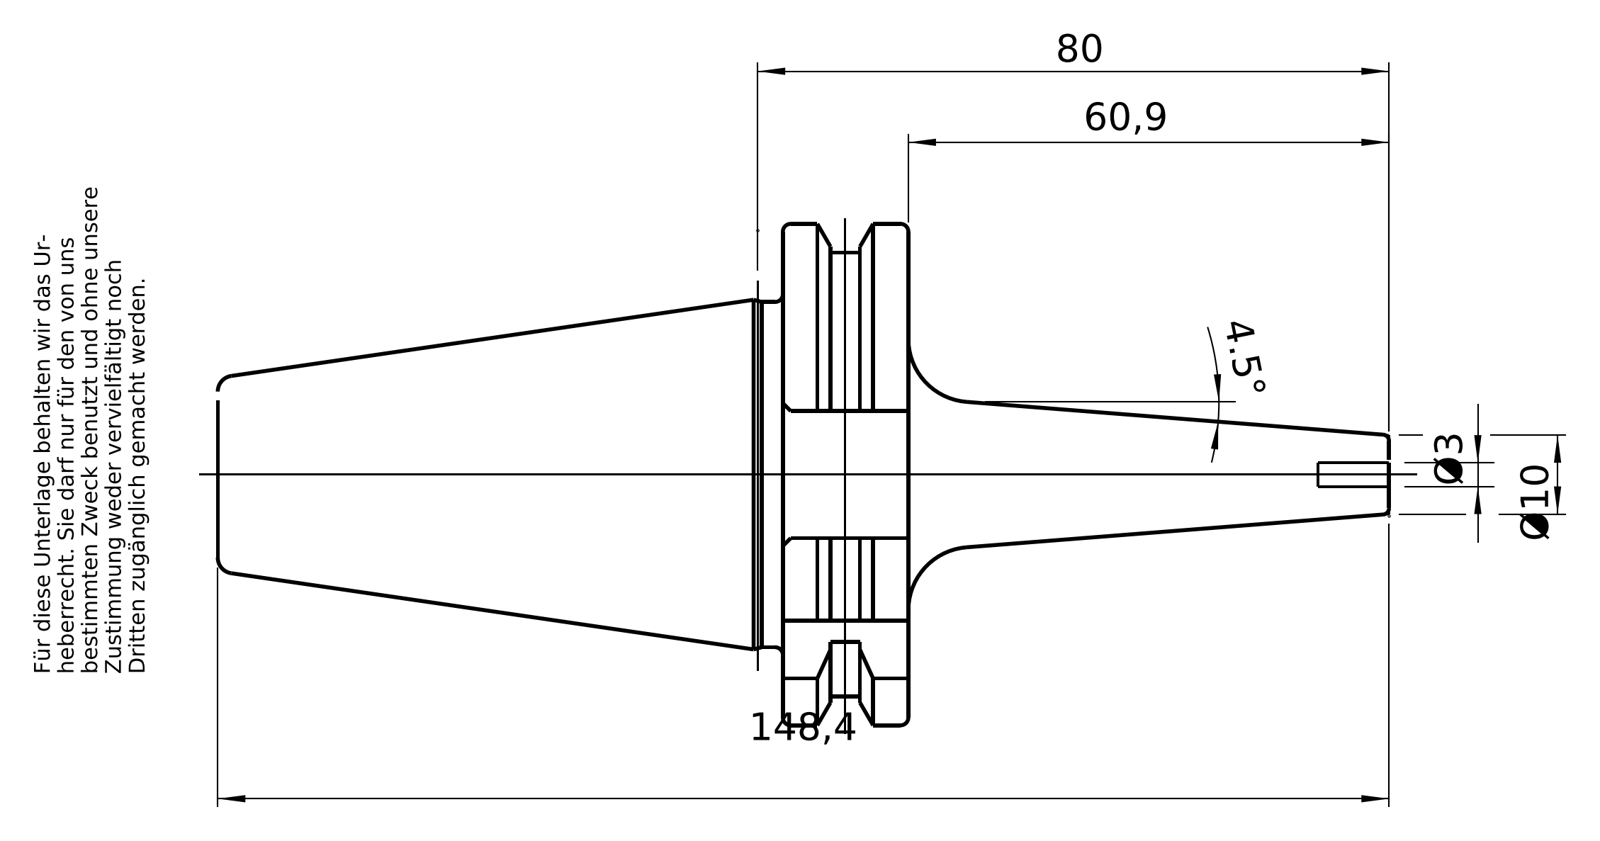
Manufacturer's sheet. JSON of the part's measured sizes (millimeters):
{"part_name": "40-440-03", "step_written_by": "PRO/ENGINEER BY PARAMETRIC TECHNOLOGY CORPORATION, 2010430 (CONFIG_CONTROL_DESIGN)", "units": "millimeters", "bodies": {"solids": 1, "faces": 95, "planar": 21, "cylindrical": 26, "other": 48}, "overall_size": [148.25, 63.52, 61.42], "volume_mm3": 117341, "surface_area_mm2": 22478, "round_holes": [[3, 1], [13.84, 1], [17.01, 1], [17.5, 1]], "round_bosses_or_shafts": [[43.75, 1], [16.01, 1]], "partial_cylinders_radius": [[1.35, 5], [28, 1], [31.76, 1]], "face_to_face_distances": [15.85, 47.4, 16.2, 71.45, 87.3, 6.5, 40.9, 10.25, 26.45, 36]}
